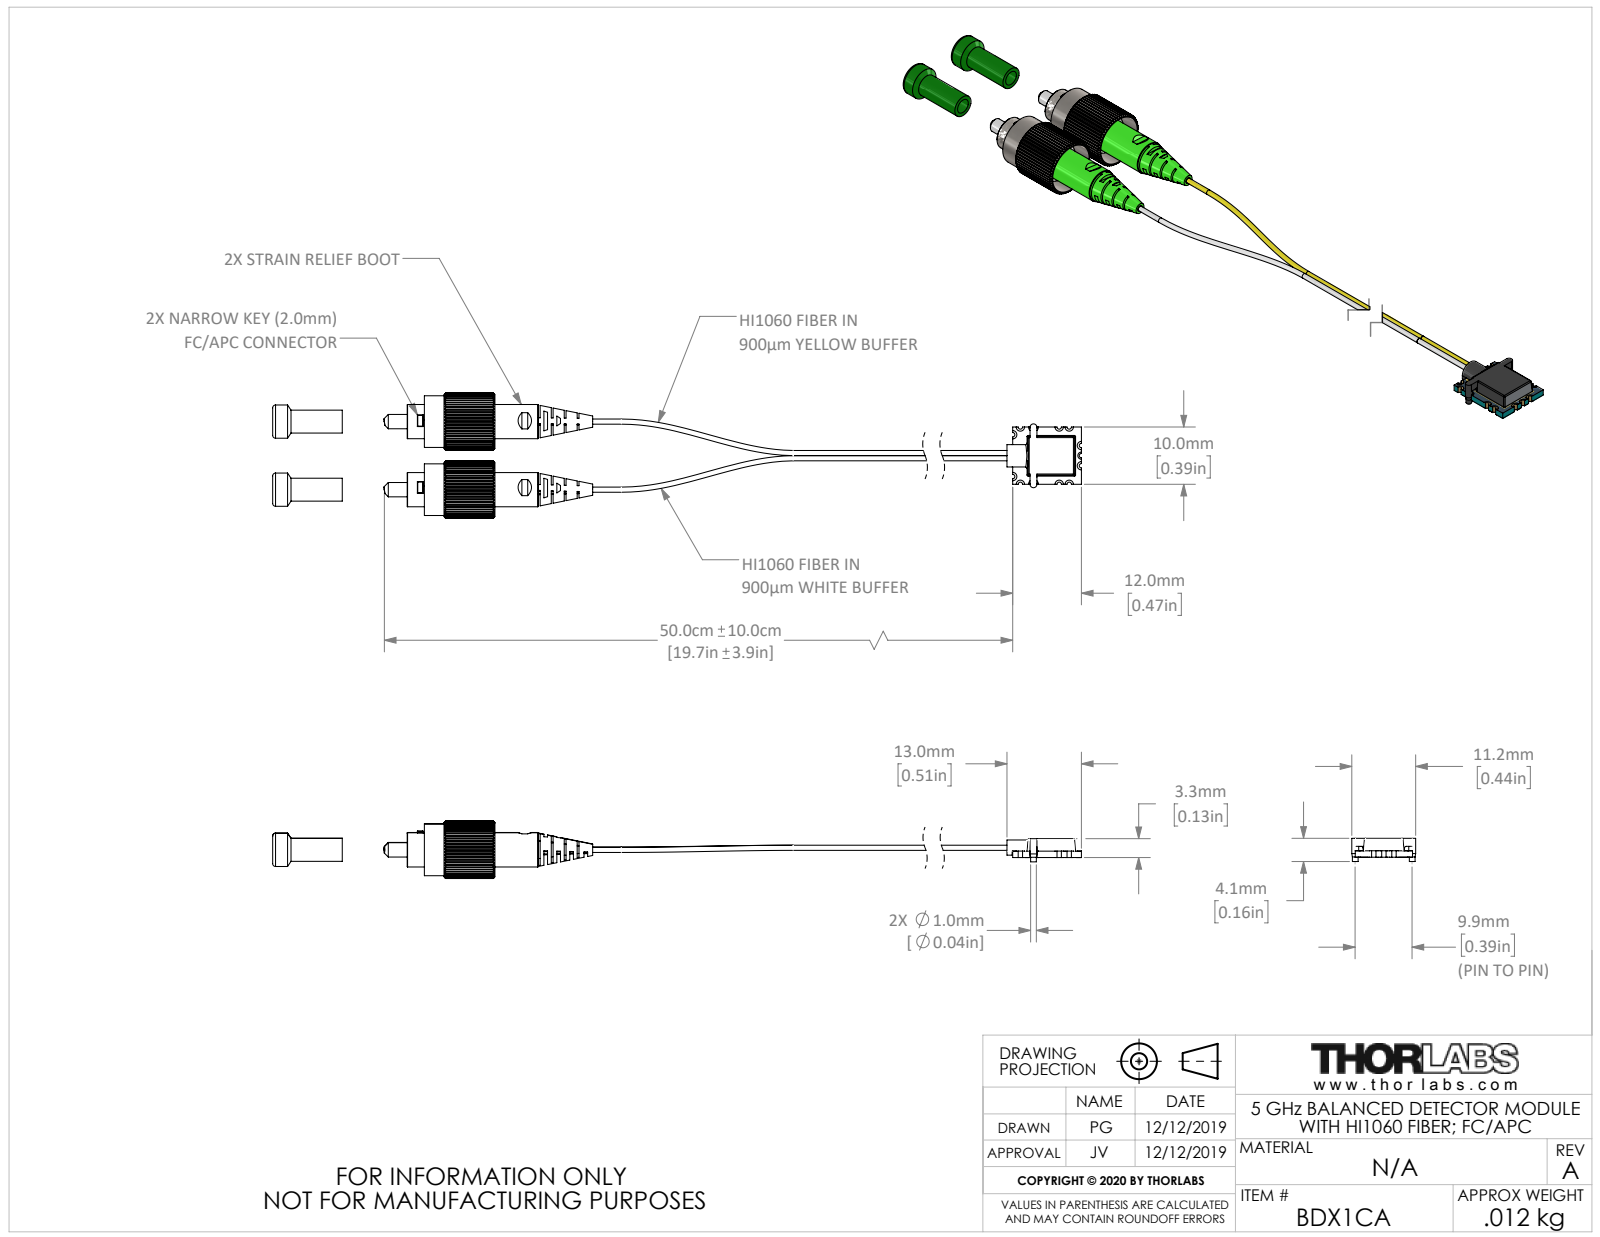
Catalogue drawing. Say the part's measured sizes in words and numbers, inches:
The part is named "BDX1CA". Its 3-D file was written by "SolidWorks 2018 (AUTOMOTIVE_DESIGN)". It is 14 solids with 903 faces: 521 planar, 299 cylindrical and 83 other. Overall it measures 7.193 by 0.862 by 0.394 inches. Its volume is 0.134 cubic inches and its surface area 9.682 square inches. Round holes: 2 of diameter 0.055, 2 of diameter 0.104, 2 of diameter 0.118, 2 of diameter 0.12, 2 of diameter 0.155, 2 of diameter 0.175, 2 of diameter 0.2, 2 of diameter 0.325, 2 of diameter 0.355, 1 of diameter 0.028. Round bosses or shafts: 4 of diameter 0.035, 2 of diameter 0.28, 2 of diameter 0.235, 2 of diameter 0.228, 2 of diameter 0.195, 2 of diameter 0.157, 2 of diameter 0.15, 2 of diameter 0.14. Partial cylindrical surfaces (rounded edges, fillets, slot ends): 11 of radius 0.015, 10 of radius 0.008, 10 of radius 0.029, 8 of radius 0.011, 3 of radius 0.025, 2 of radius 0.012, 2 of radius 0.025, 2 of radius 0.034. The main face-to-face distances are 0.267, 0.267, 0.044, 0.062, 0.04, 0.02, 0.102, 0.089, 0.013, 0.13. The hole center spacings are 0.469.
